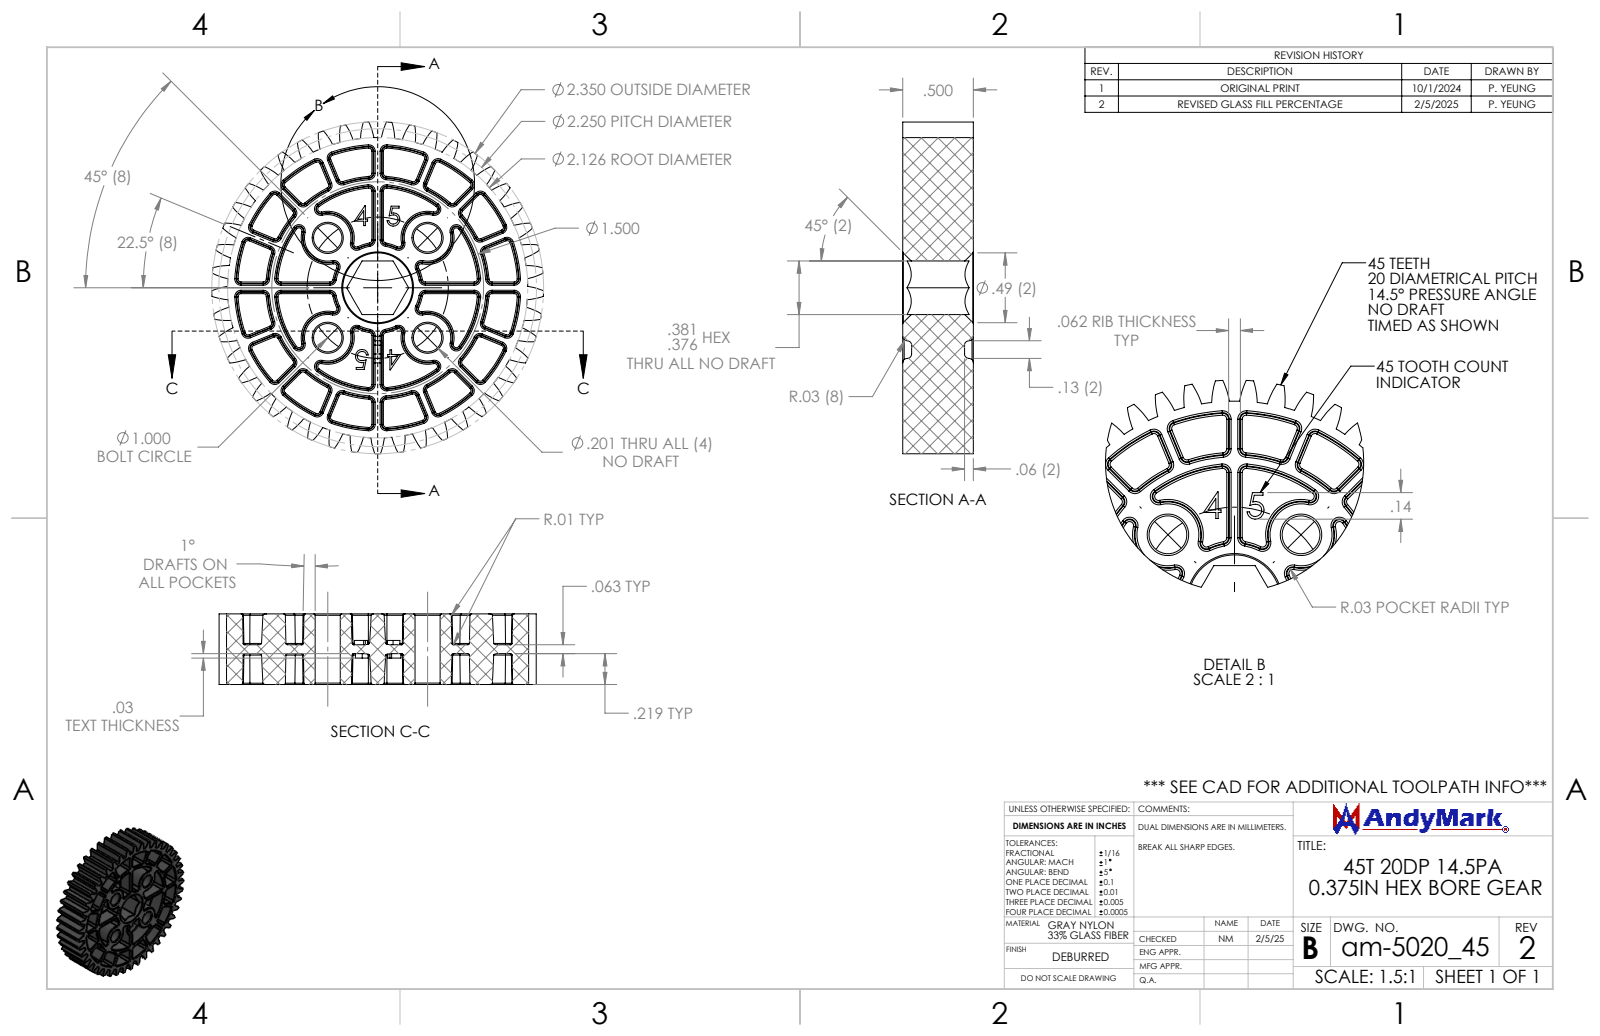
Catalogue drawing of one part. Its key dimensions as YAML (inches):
part_name: "am-5020_45 45T 20DP 14.5PA 0.50 IN FW 0.375 Hex Gear"
step_written_by: "SolidWorks 2024 (AUTOMOTIVE_DESIGN)"
units: inches
bodies: {solids: 1, faces: 1739, planar: 226, cylindrical: 368, other: 1145}
overall_size: [2.35, 2.348, 0.5]
volume: 1.034
surface_area: 27.81
round_holes:
  - {diameter: 0.201, count: 4}
partial_cylinders:
  - {radius: 0.45, count: 90}
  - {radius: 0.01, count: 75}
  - {radius: 0.031, count: 8}
  - {radius: 1.063, count: 1}
  - {radius: 1.175, count: 1}
face_to_face_distances: [0.219, 0.281, 0.064, 0.062, 0.5, 0.38, 0.031, 0.187, 0.313, 0.094]
hole_center_spacings: [0.707, 1]
